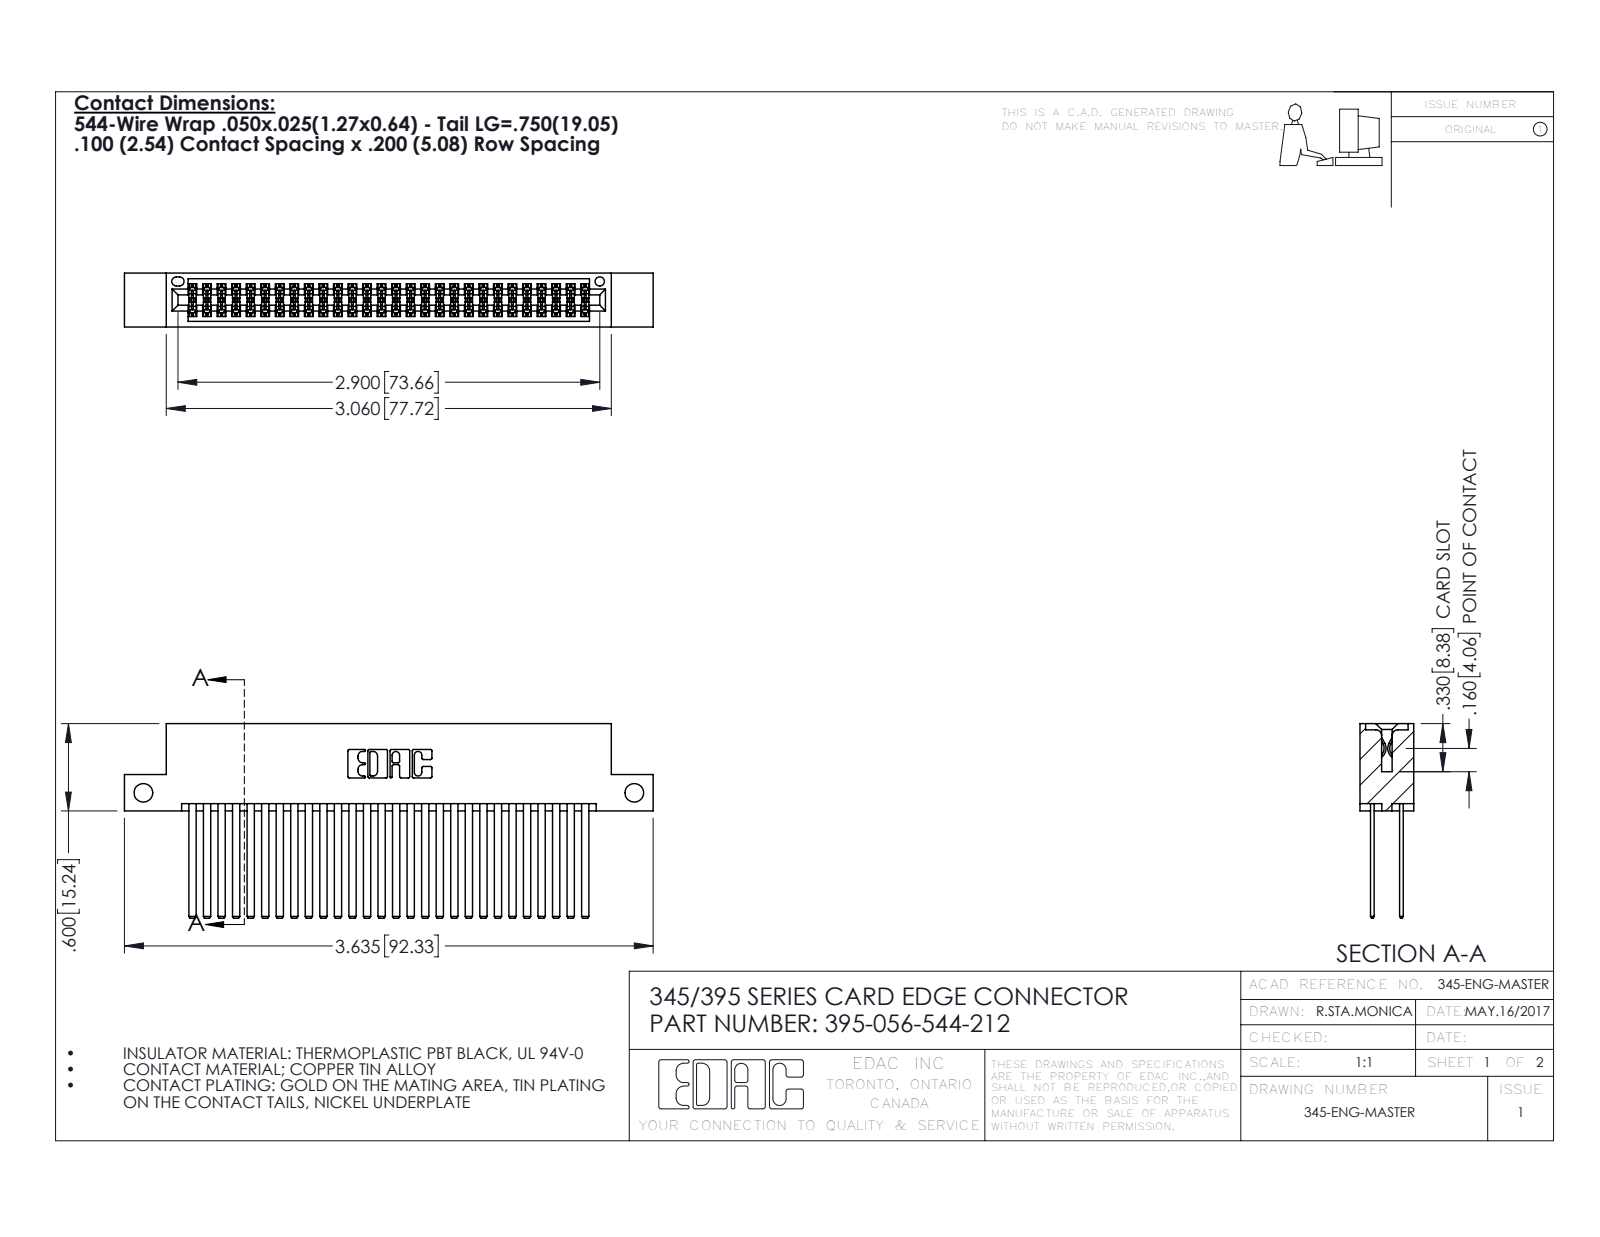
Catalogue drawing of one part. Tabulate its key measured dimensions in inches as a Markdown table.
| quantity | value |
| --- | --- |
| part name | 395-056-544-212; 345 Part_Flush Mounting Lugs - Side Mount; 345-292-001_345-293-144 |
| STEP written by | SolidWorks 2016 (CONFIG_CONTROL_DESIGN) |
| units | inches |
| bodies | 57 solids, 2590 faces (1704 planar, 886 cylindrical, 0 other) |
| overall size | 3.635 × 1.337 × 0.37 |
| volume | 0.582 in³ |
| surface area | 24.79 in² |
| round holes (diameter × count) | 0.128 × 2, 0.064 × 1 |
| partial cylindrical surfaces (radius × count) | 0.006 × 84, 0.01 × 22, 0.007 × 6, 0.031 × 6, 0.026 × 3, 0.014 × 2, 0.019 × 2, 0.022 × 2 |
| main face-to-face distances | 0.2, 0.025, 0.298, 0.072, 0.098, 0.272, 0.225, 0.175, 0.37, 0.05 |
| hole center spacings | 3.375 |
